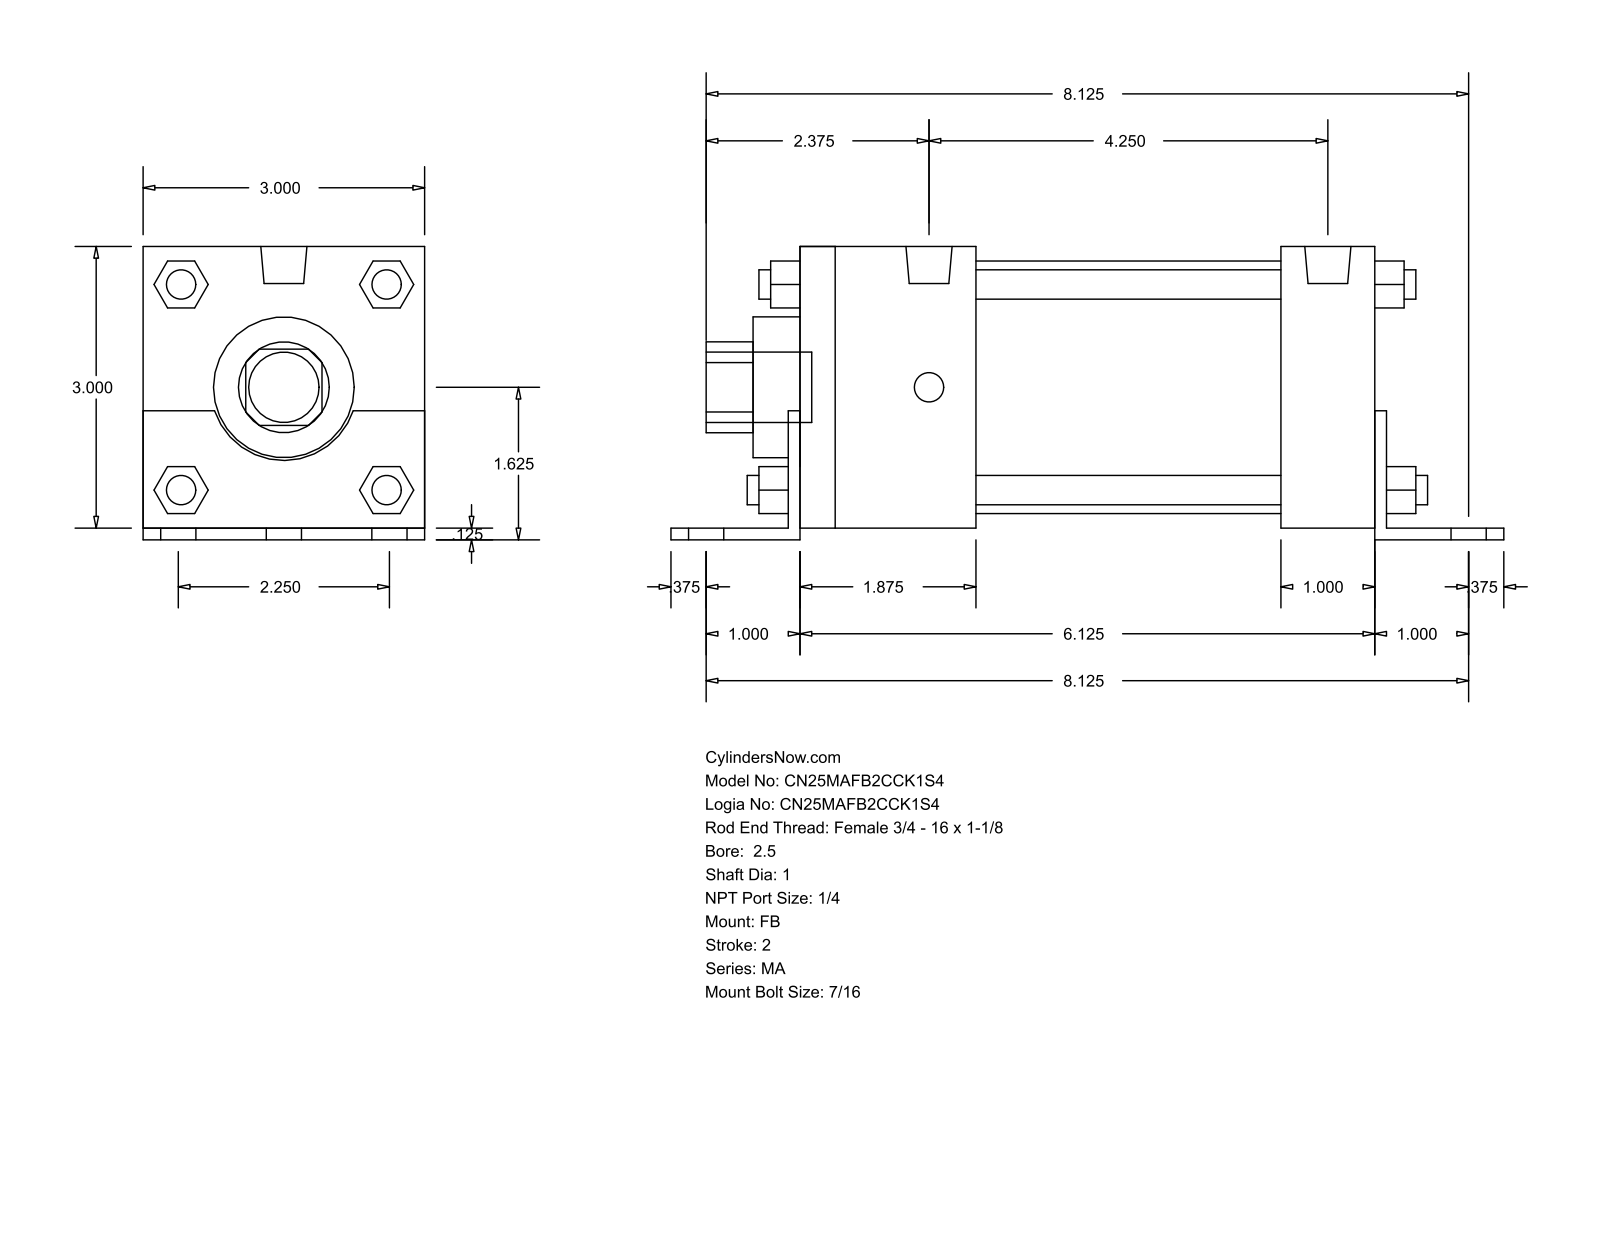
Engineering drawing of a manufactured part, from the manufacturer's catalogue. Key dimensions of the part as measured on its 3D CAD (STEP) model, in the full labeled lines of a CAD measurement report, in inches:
Part name (STEP PRODUCT): MA_FB__0250_1
STEP written by: GSSL Pune (CONFIG_CONTROL_DESIGN)
Units: inches
Bodies: 0 solids, 140 faces (105 planar, 35 cylindrical, 0 other)
Overall size (bounding box): 8.875 × 3.125 × 3
Round holes (diameter × count): ⌀1 ×1, ⌀1.5 ×1, ⌀2.69 ×1
Round bosses / shafts (diameter × count): ⌀0.313 ×8, ⌀0.437 ×6, ⌀0.492 ×2, ⌀0.75 ×1
Partial cylindrical surfaces — rounded edges, fillets, slot ends (radius × count): R0.484 ×1, R0.78 ×1
Main face-to-face distances: 3, 0.125, 3.125, 6.125, 0.125, 0.5, 6.25, 1, 1.875, 4.25
